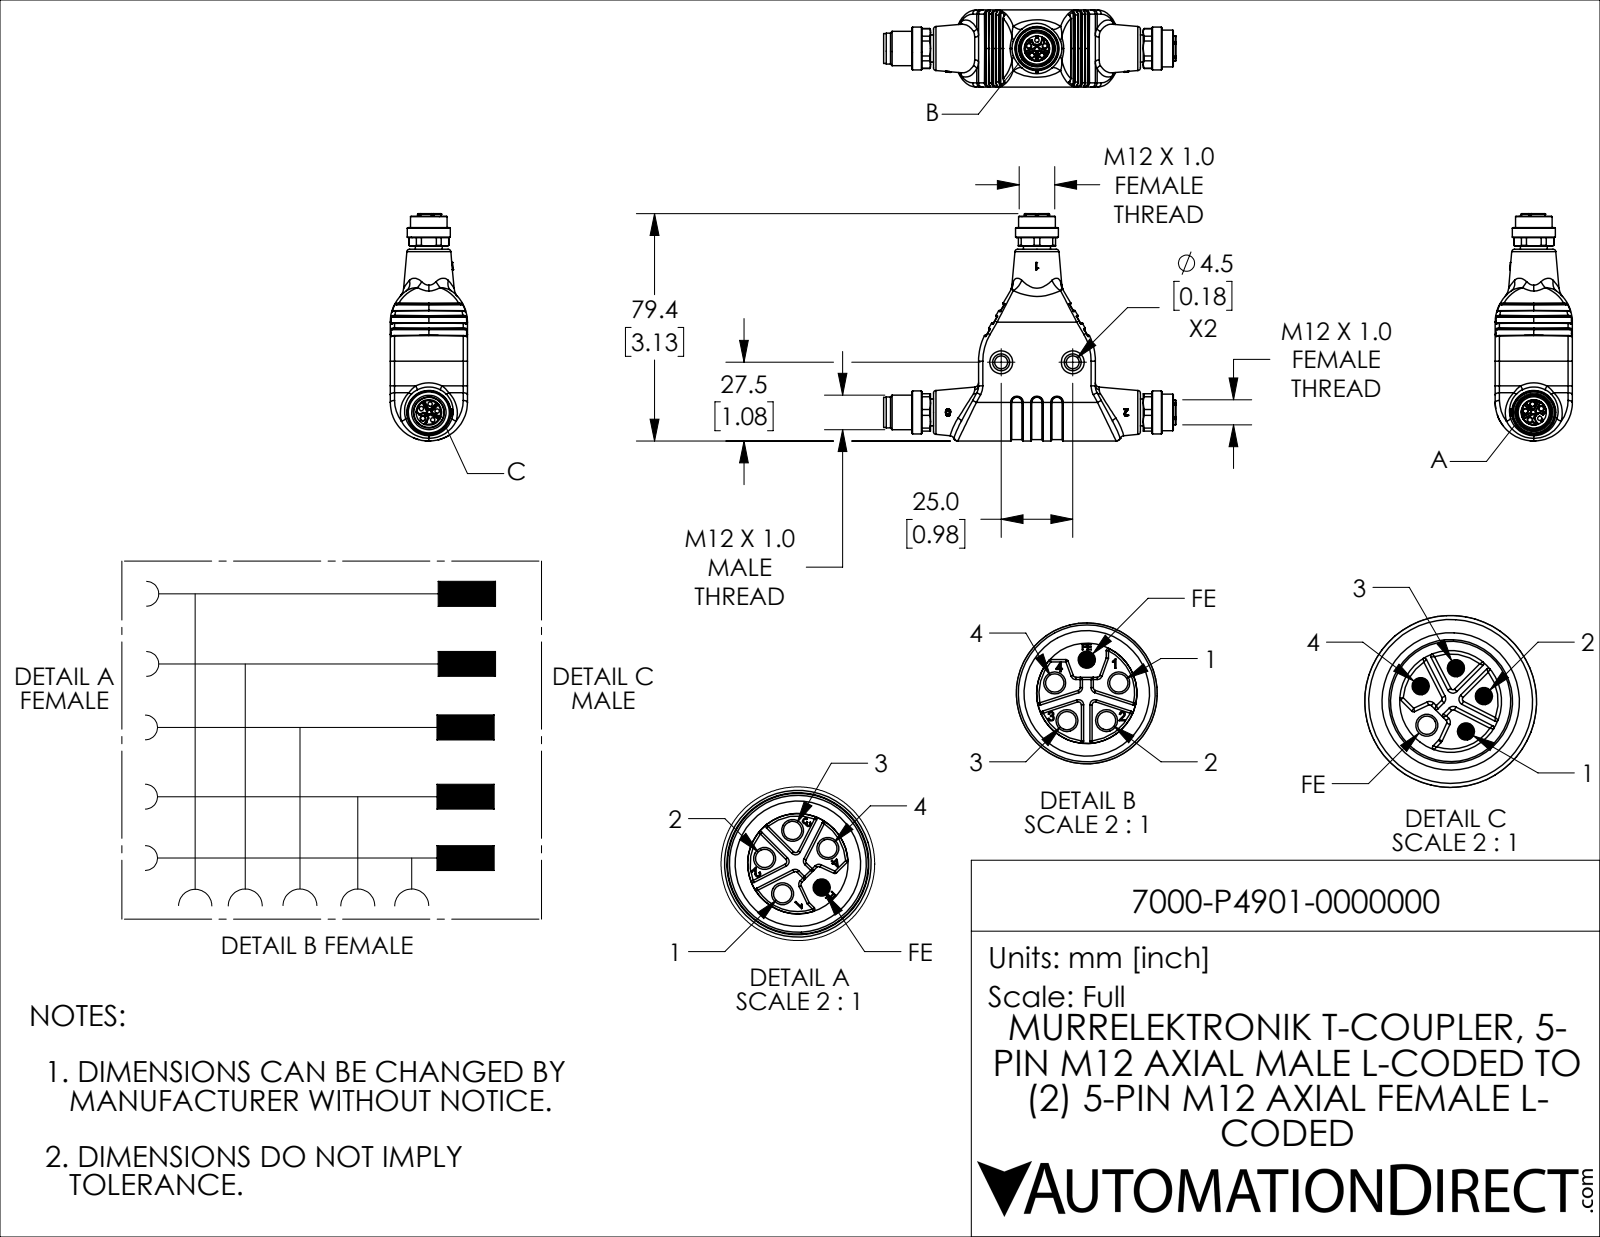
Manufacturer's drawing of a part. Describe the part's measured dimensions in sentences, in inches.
The part is named "7000-P4901-0000000". Its 3-D file was written by "SolidWorks 2021 (CONFIG_CONTROL_DESIGN)". It is 1 solid with 958 faces: 288 planar, 292 cylindrical and 378 other. Overall it measures 4.02 by 3.125 by 1.061 inches. Its volume is 3.728 cubic inches and its surface area 23.05 square inches. Round holes: 9 of diameter 0.063, 2 of diameter 0.177, 2 of diameter 0.315, 2 of diameter 0.431, 2 of diameter 0.484, 1 of diameter 0.35. Round bosses or shafts: 6 of diameter 0.059, 2 of diameter 0.591, 2 of diameter 0.504, 2 of diameter 0.37, 1 of diameter 0.472, 1 of diameter 0.425, 1 of diameter 0.413. Partial cylindrical surfaces (rounded edges, fillets, slot ends): 64 of radius 0.008, 44 of radius 0.008, 13 of radius 0.012, 12 of radius 0.058, 8 of radius 0.018, 4 of radius 0.01, 4 of radius 0.02, 3 of radius 0.079. The main face-to-face distances are 1.061, 1.606, 0.039, 0.62, 2.226, 0.512, 0.659, 2.266, 2.886, 0.295. The hole center spacings are 0.116, 0.136, 0.22, 0.136, 0.22, 0.984.
